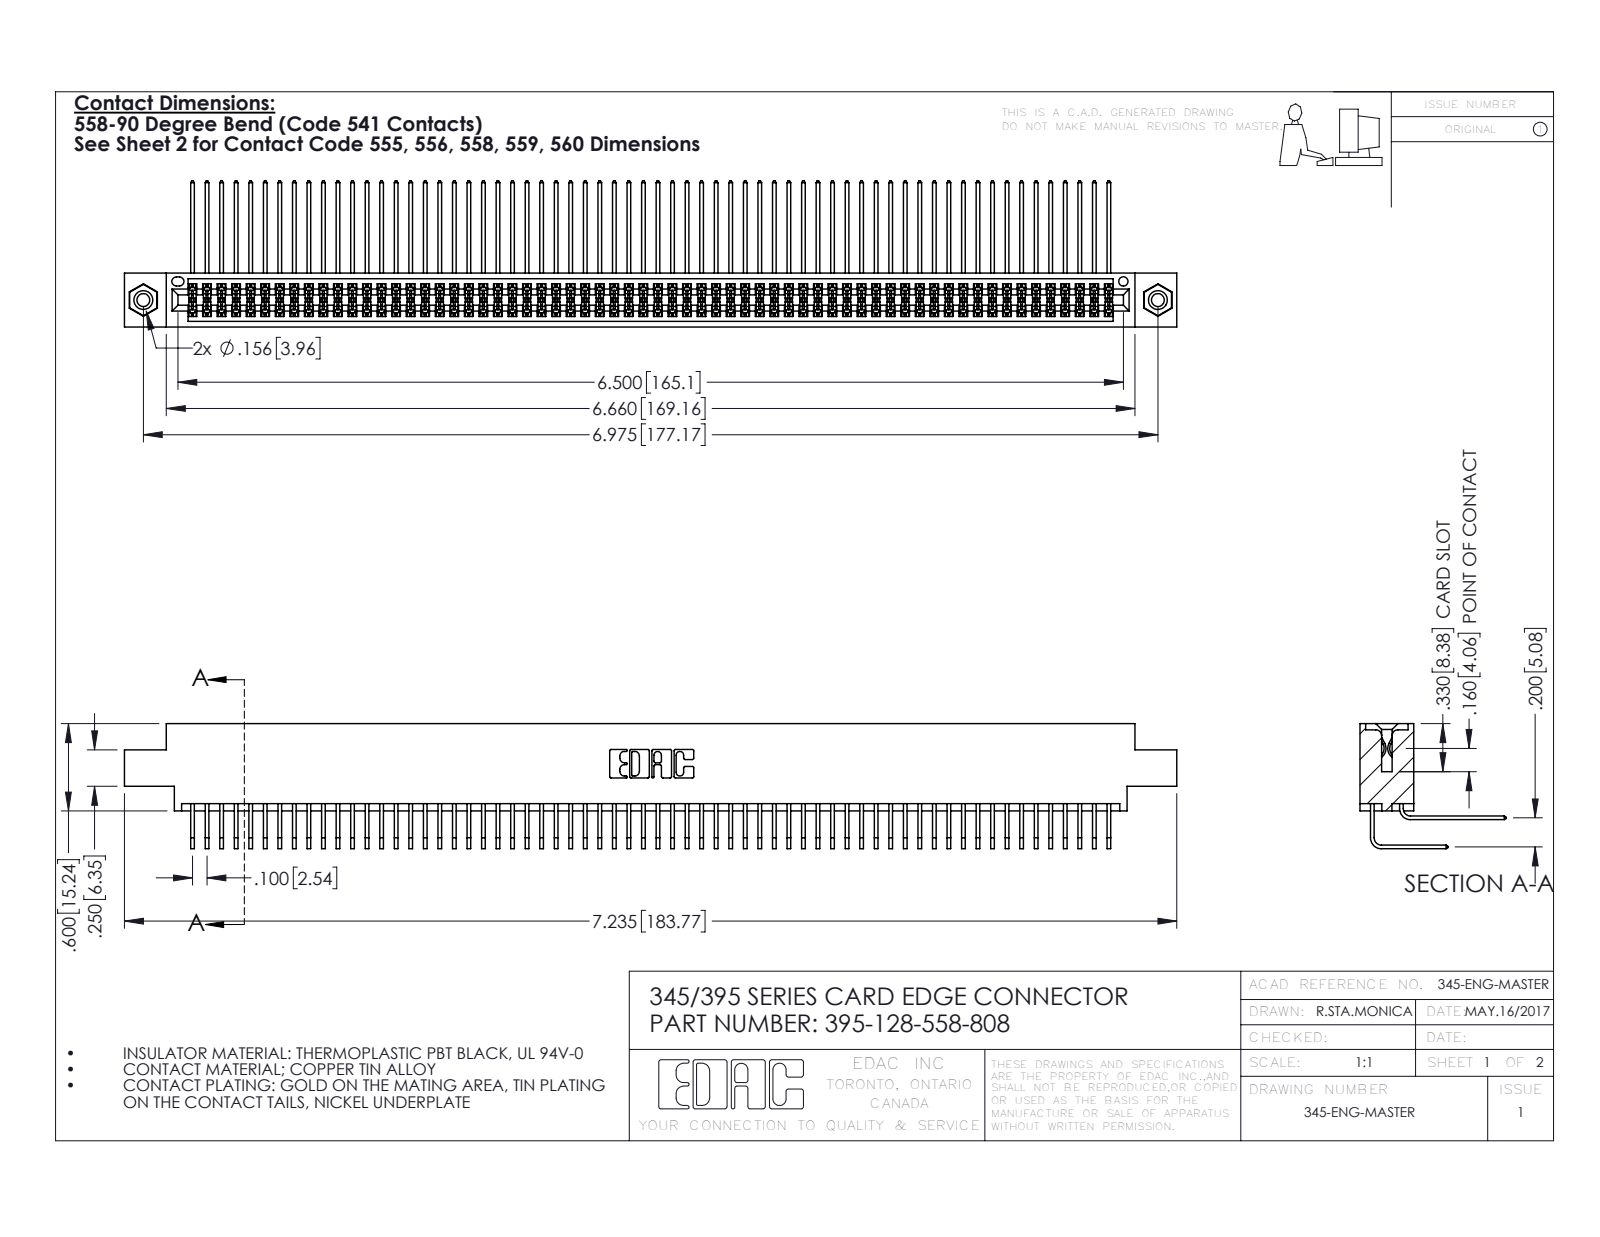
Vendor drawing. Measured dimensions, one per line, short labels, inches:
name: 345-250-001_345-250-003-102; 345-292-001_558 559 Tail - 1; 395-128-558-808; 345-292-001_558 Tail - 2 (+1 more)
written by: SolidWorks 2016 (CONFIG_CONTROL_DESIGN)
unit: in
bodies: 131 solids, 6846 faces (4596 planar, 2234 cylindrical, 16 other)
size: 7.235 × 1.005 × 0.859
volume: 1.14 in³; area: 49.07 in²
holes: 2× ⌀0.089, 2× ⌀0.125, 2× ⌀0.156, 1× ⌀0.064
bosses: 2× ⌀0.155
rounds: 193× R0.006, 22× R0.01, 6× R0.007, 6× R0.031, 3× R0.026, 2× R0.014, 2× R0.019, 2× R0.022
face distances: 0.072, 0.298, 0.2, 0.37, 0.098, 0.272, 0.025, 0.225, 0.175, 0.025
hole spacings: 0.27, 6.739, 6.975
